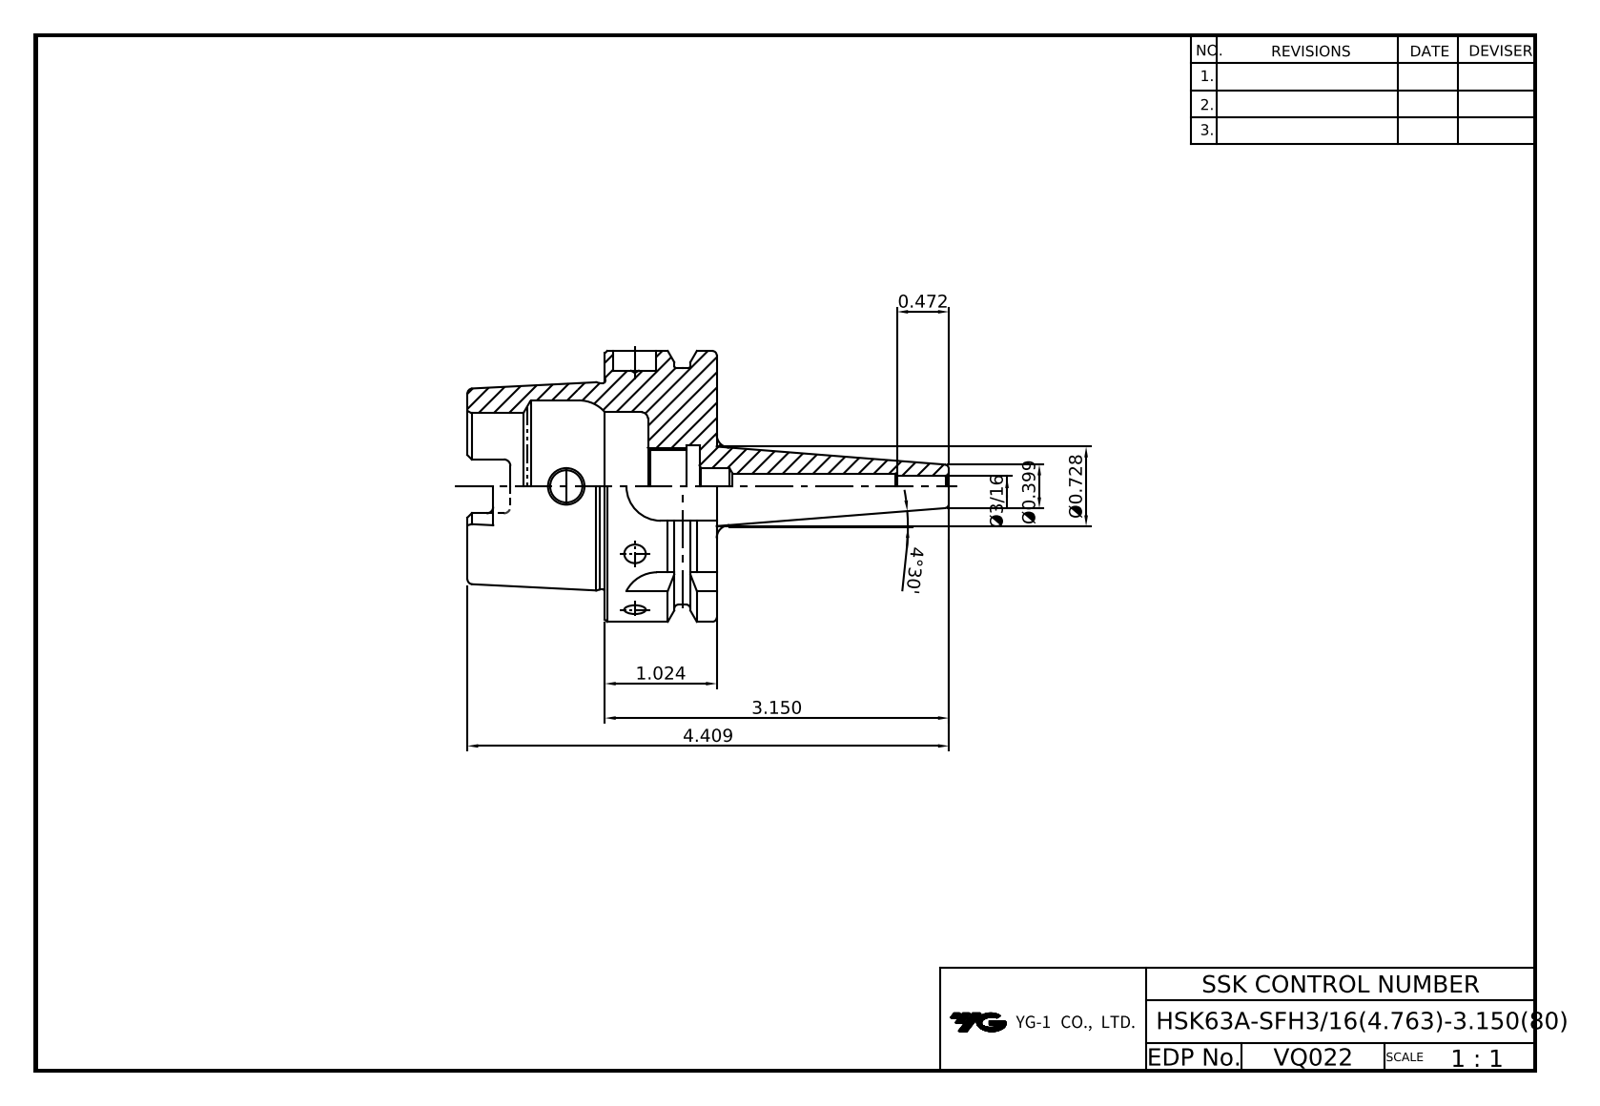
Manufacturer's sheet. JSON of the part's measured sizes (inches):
{"part_name": "LO-HSK63A-SFH4.7625-80", "step_written_by": "Autodesk Inventor 2022 (AUTOMOTIVE_DESIGN)", "units": "inches", "bodies": {"solids": 1, "faces": 113, "planar": 40, "cylindrical": 32, "other": 41}, "overall_size": [4.409, 2.48, 2.48], "volume_in3": 5.426, "surface_area_in2": 39.52, "round_holes": [[0.187, 1], [0.236, 1], [0.295, 1], [0.331, 1], [0.394, 1], [0.666, 1], [0.748, 1], [1.339, 1], [1.575, 1]], "round_bosses_or_shafts": [[2.48, 1], [2.165, 1], [1.891, 1]], "partial_cylinders_radius": [[0.059, 6], [0.113, 4], [0.315, 4]], "face_to_face_distances": [1.024, 0.394, 0.63, 1.26, 2.283, 1.654, 2.087, 0.866, 0.157, 0.472]}
